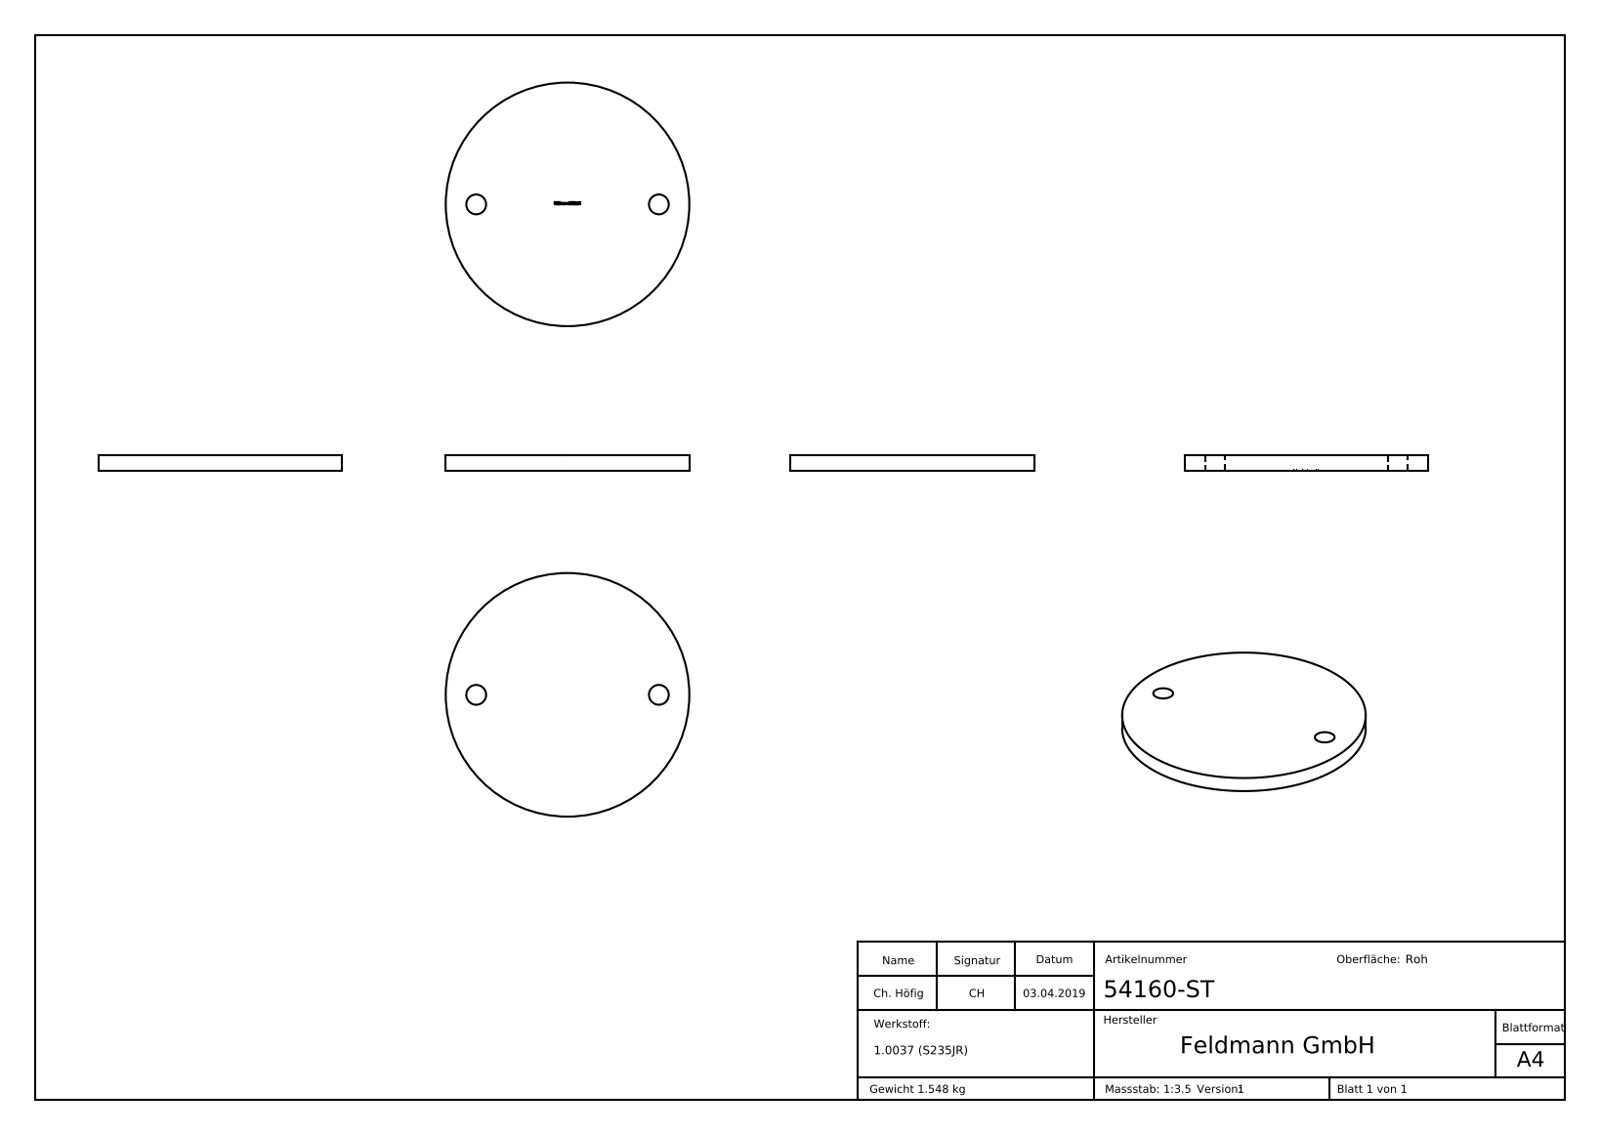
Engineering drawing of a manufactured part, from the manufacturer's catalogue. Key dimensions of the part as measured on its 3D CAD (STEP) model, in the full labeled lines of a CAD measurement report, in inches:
Part name (STEP PRODUCT): 54160-ST
STEP written by: SolidWorks 2015 (CONFIG_CONTROL_DESIGN)
Units: inches
Bodies: 1 solid, 215 faces (120 planar, 6 cylindrical, 89 other)
Overall size (bounding box): 6.299 × 6.299 × 0.394
Volume: 12.11 in³ · Surface area: 70.58 in²
Round holes (diameter × count): ⌀0.512 ×2
Round bosses / shafts (diameter × count): ⌀6.299 ×1
Main face-to-face distances: 0.394, 0.39, 0.201, 0.17, 0.015, 0.383, 0.08, 0.462, 0.052, 0.174
Hole centre spacings: 4.724
